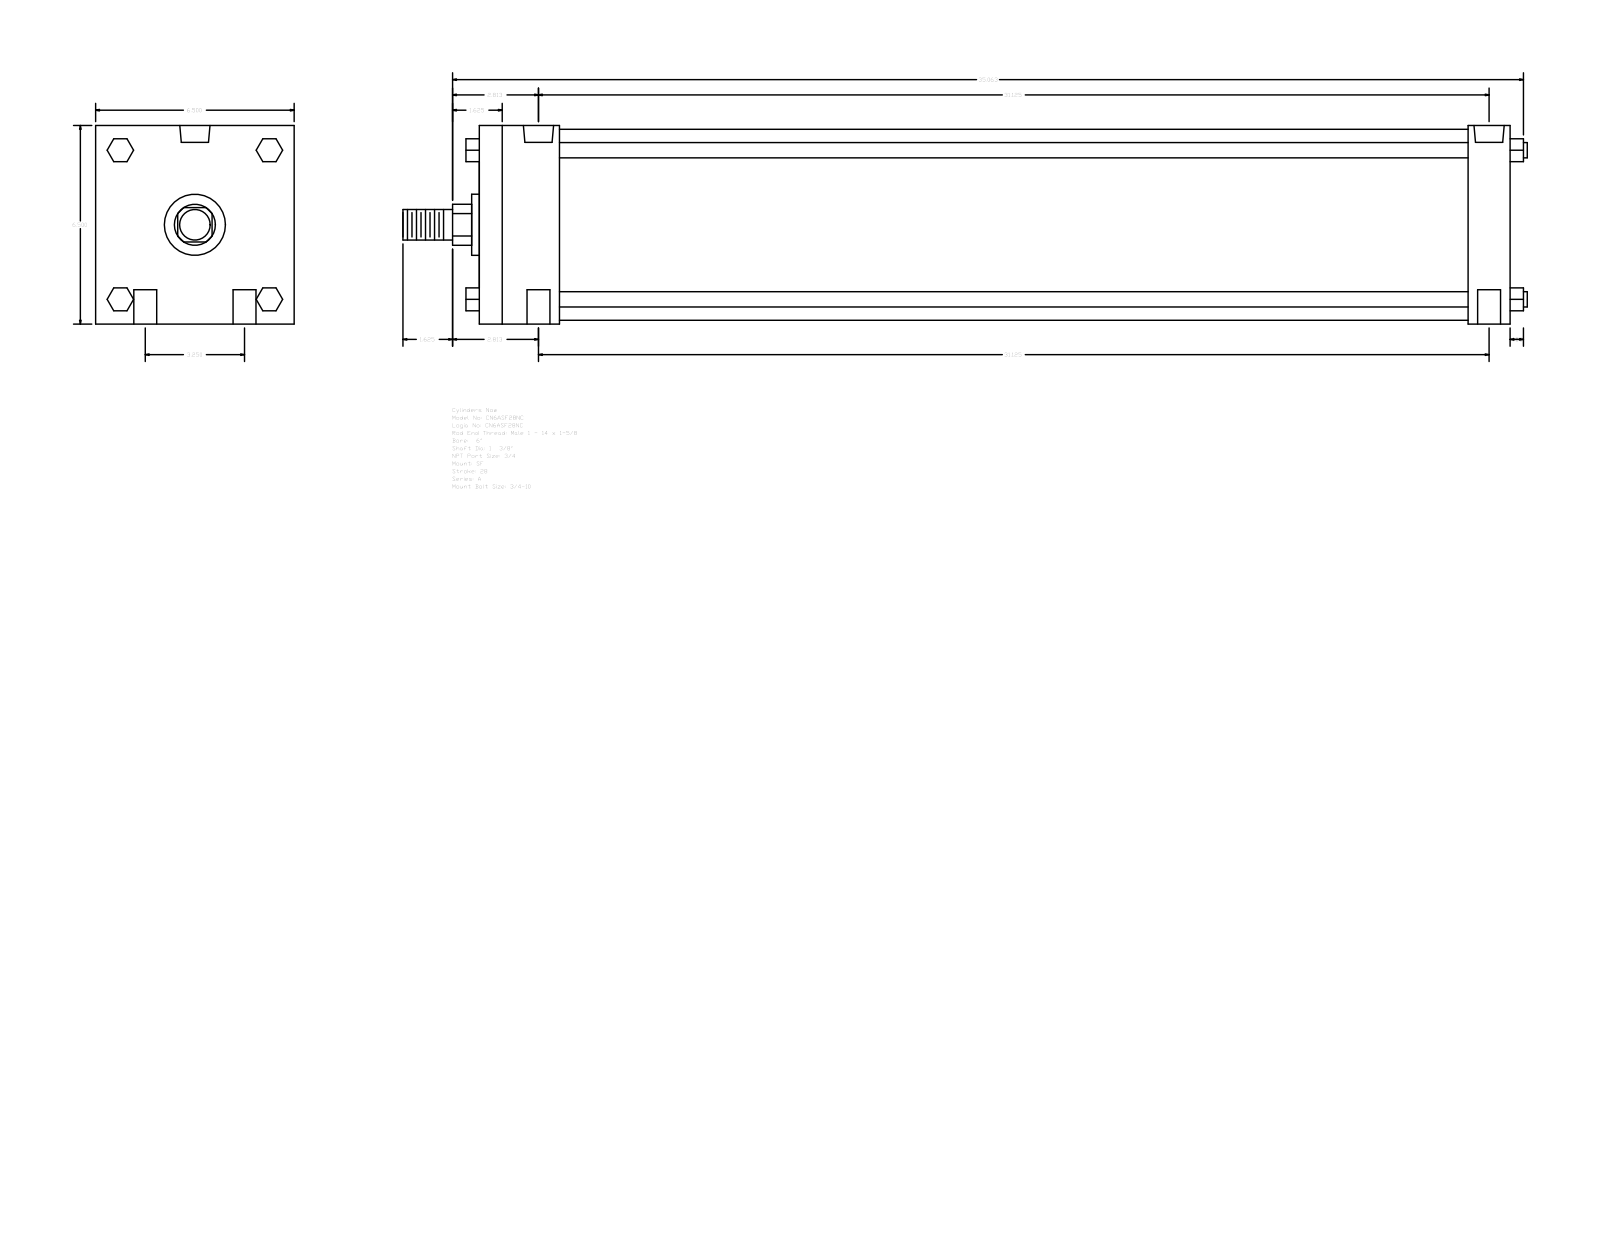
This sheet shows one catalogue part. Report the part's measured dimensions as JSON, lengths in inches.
{"part_name": "A_SF__0600_1.375", "step_written_by": "GSSL Pune (CONFIG_CONTROL_DESIGN)", "units": "inches", "bodies": {"solids": 0, "faces": 124, "planar": 94, "cylindrical": 30, "other": 0}, "overall_size": [36.813, 6.5, 6.5], "round_holes": [[0.75, 4], [0.594, 2], [0.989, 2]], "round_bosses_or_shafts": [[0.5, 4], [6.25, 1], [2, 1], [1.375, 1], [1, 1]], "partial_cylinders_radius": [[0.672, 1]], "face_to_face_distances": [6.5, 33.75, 32.375, 1.375, 2.625, 29.75, 31.125, 0.75, 2.44, 4.226], "hole_center_spacings": [1.625, 31.167, 31.125, 3.25, 31.294, 30.687]}
